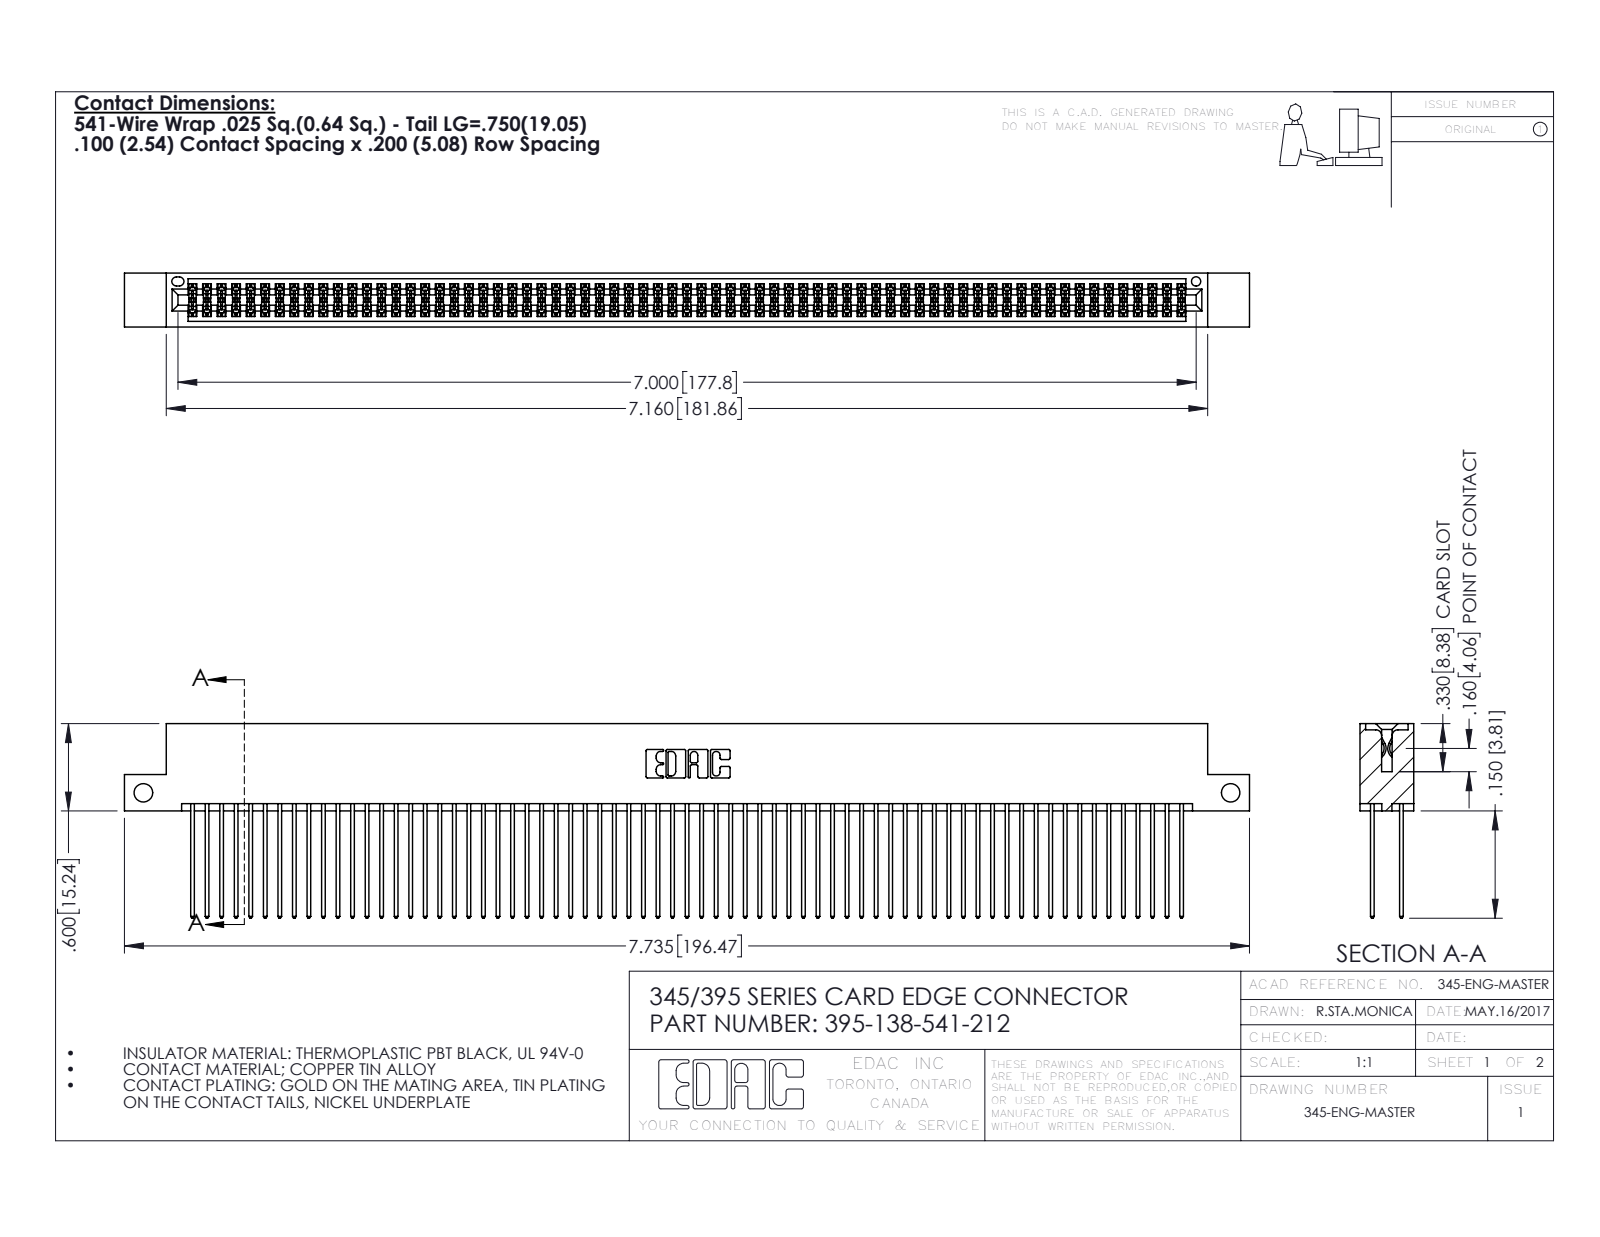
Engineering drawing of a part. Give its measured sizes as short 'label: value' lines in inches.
name: 395-138-541-212; 345 Part_Flush Mounting Lugs - Side Mount; 345-292-001_345-293-141
written by: SolidWorks 2016 (CONFIG_CONTROL_DESIGN)
unit: in
bodies: 139 solids, 7026 faces (4634 planar, 2392 cylindrical, 0 other)
size: 7.735 × 1.337 × 0.37
volume: 1.223 in³; area: 52.28 in²
holes: 2× ⌀0.128, 1× ⌀0.064
rounds: 207× R0.006, 138× R0.01, 22× R0.01, 6× R0.007, 6× R0.031, 3× R0.026, 2× R0.014, 2× R0.019
face distances: 0.298, 0.072, 0.2, 0.098, 0.272, 0.025, 0.225, 0.37, 0.175, 0.149
hole spacings: 7.475
